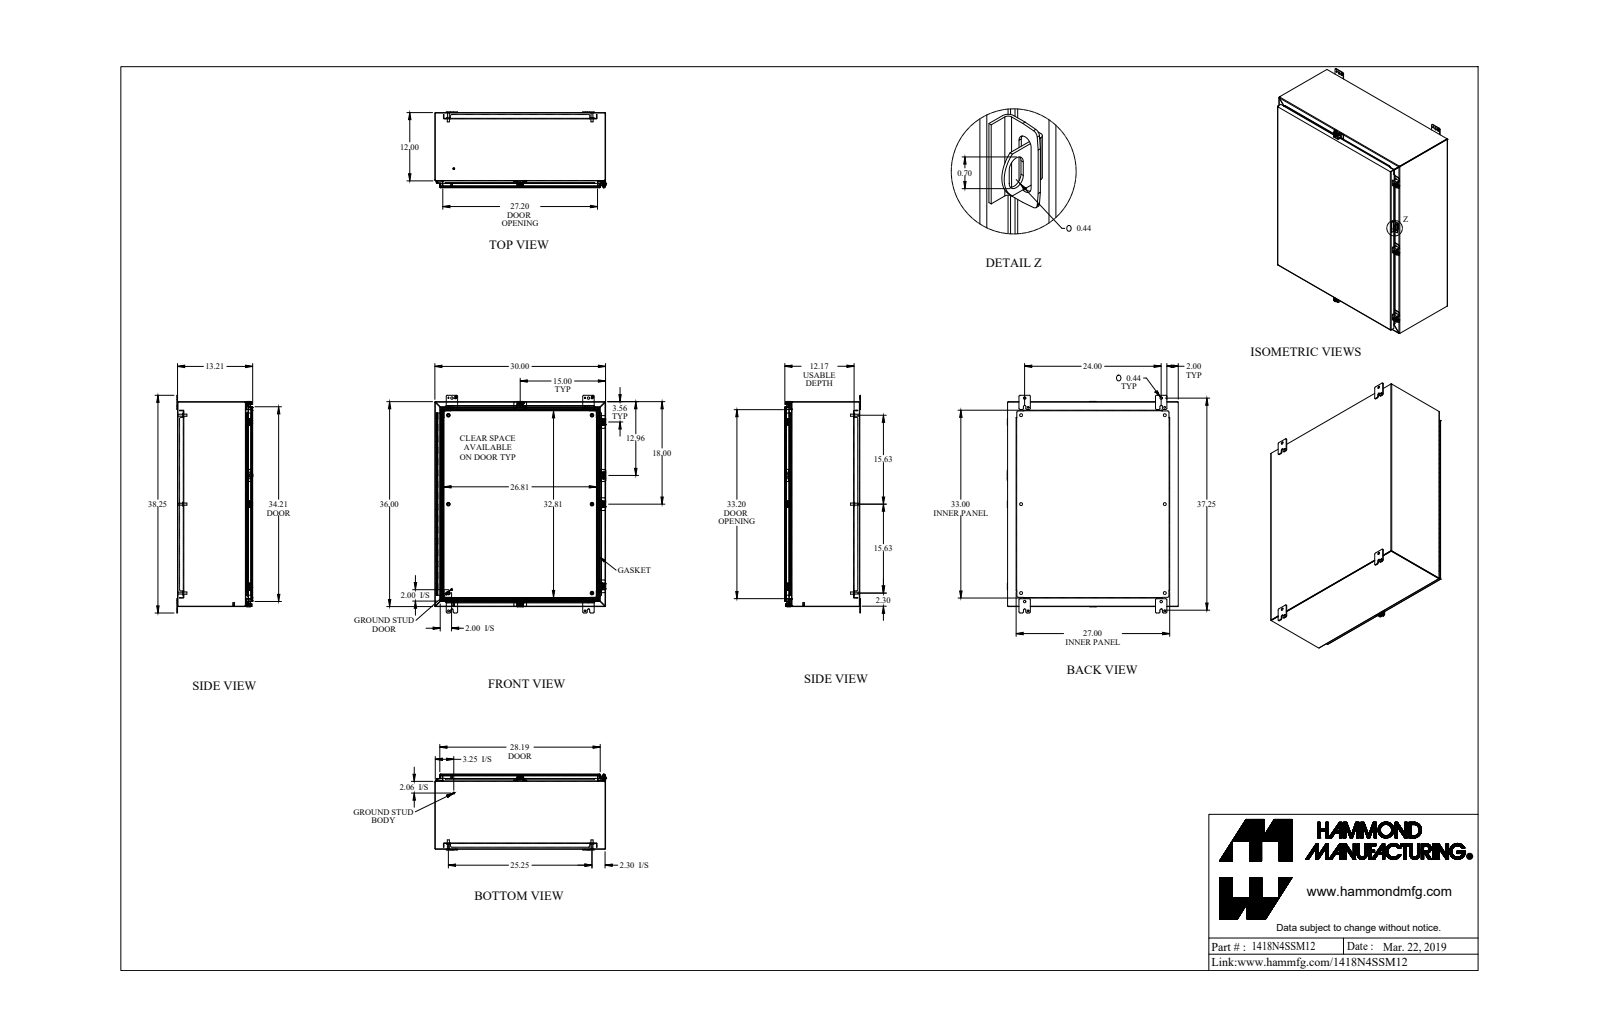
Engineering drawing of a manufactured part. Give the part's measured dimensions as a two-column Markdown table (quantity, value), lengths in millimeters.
| quantity | value |
| --- | --- |
| part name | 1418N4SSM12_Default |
| STEP written by | SolidWorks 2019 (CONFIG_CONTROL_DESIGN) |
| units | millimeters |
| bodies | 53 solids, 1825 faces (1095 planar, 632 cylindrical, 98 other) |
| overall size | 971.6 × 763.6 × 339.7 |
| volume | 6 612 000 mm³ |
| surface area | 6 831 000 mm² |
| round holes (diameter × count) | 12.7 × 6, 5.4 × 5, 6.7 × 5, 7.8 × 5, 8 × 4, 9.5 × 4, 11.1 × 4, 11.3 × 3, 11.3 × 2, 3.2 × 1, 4.7 × 1, 9.5 × 1 |
| round bosses / shafts (diameter × count) | 16.5 × 6, 9.5 × 6, 8.4 × 6, 25.4 × 5, 12.7 × 5, 9.9 × 5, 6.2 × 5, 8 × 2 |
| partial cylindrical surfaces (radius × count) | 6.4 × 36, 1.2 × 27, 3.6 × 27, 4.8 × 26, 0.9 × 22, 2.7 × 22, 3.2 × 12, 3.6 × 10 |
| main face-to-face distances | 1.8, 1.8, 331.9, 333.7, 333.7, 335.5, 23.8, 307.5, 305.7, 26.2 |
| hole center spacings | 1020.5, 396.9, 641.4, 305.6, 325.2, 325.2, 553.3, 609.6 |
